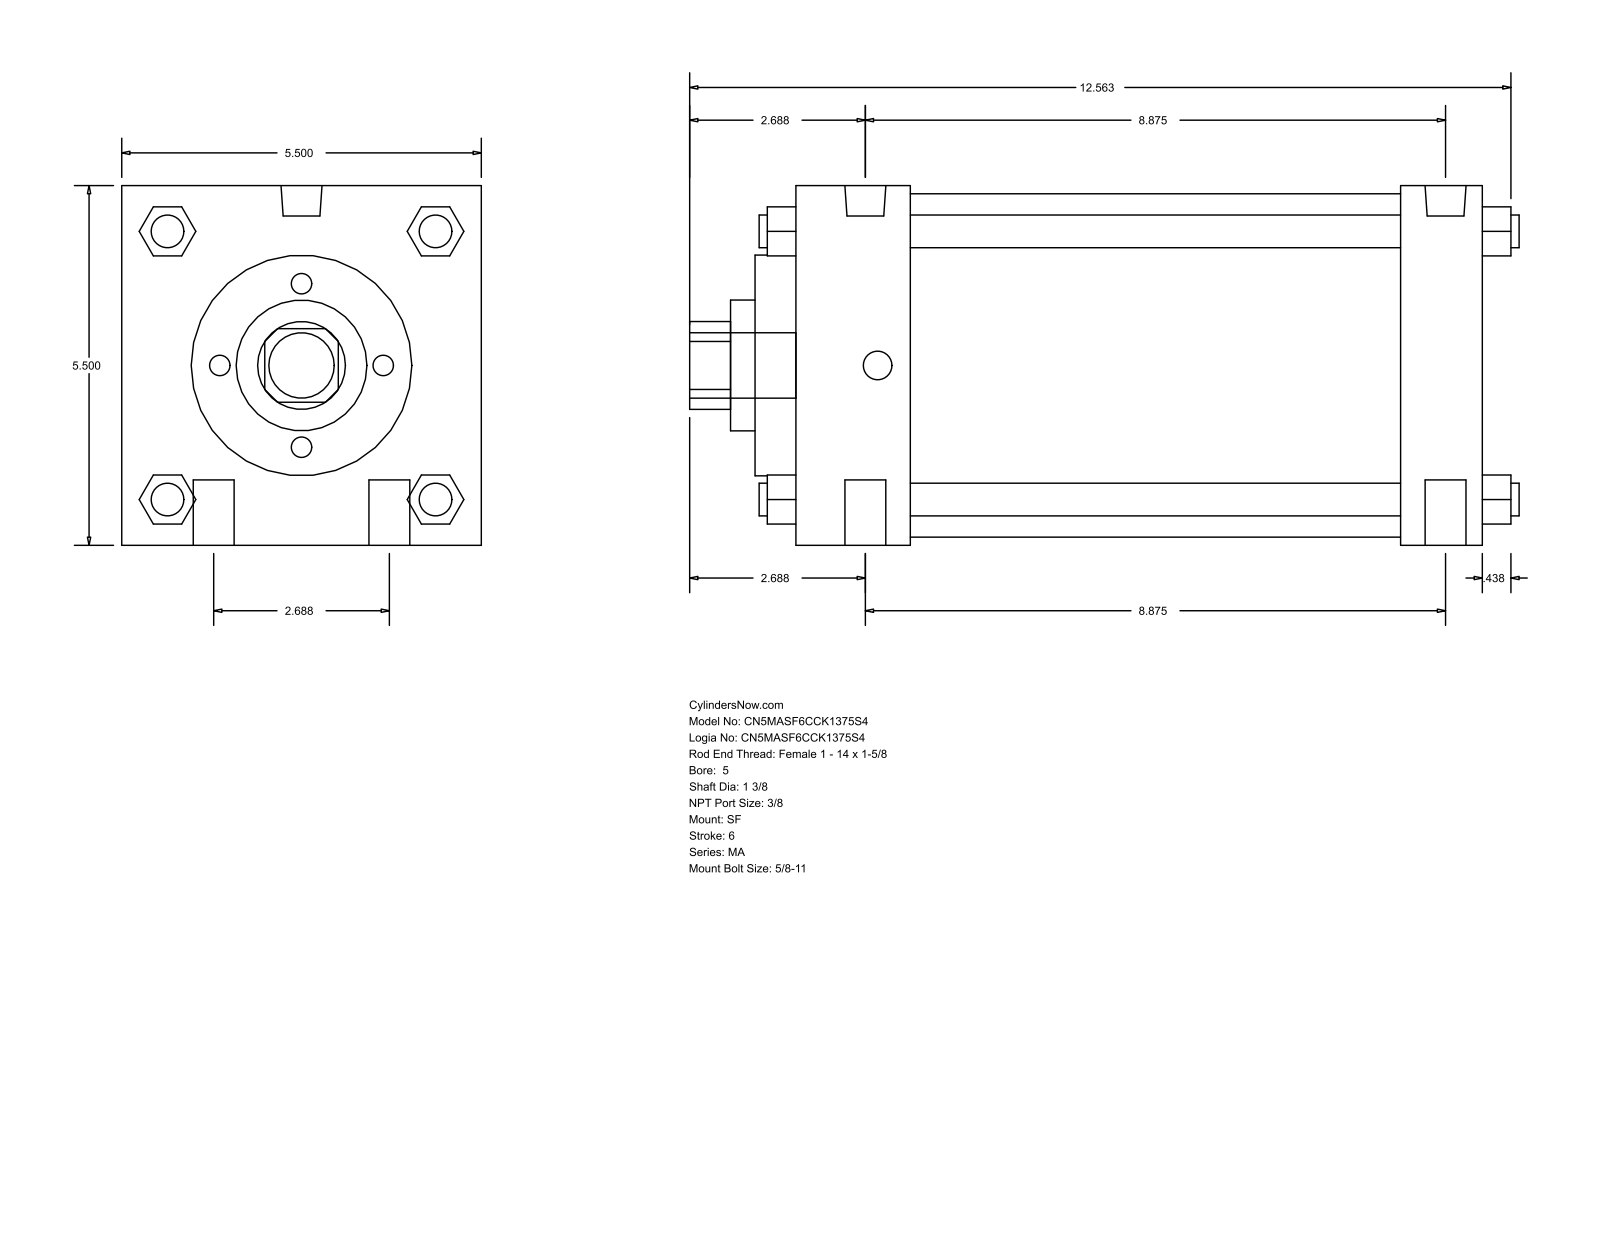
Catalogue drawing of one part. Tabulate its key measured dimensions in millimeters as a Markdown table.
| quantity | value |
| --- | --- |
| part name | MA_SF__0500_1.375 |
| STEP written by | GSSL Pune (CONFIG_CONTROL_DESIGN) |
| units | millimeters |
| bodies | 0 solids, 126 faces (95 planar, 31 cylindrical, 0 other) |
| overall size | 322.26 × 139.7 × 139.7 |
| round holes (diameter × count) | 34.92 × 1, 50.8 × 1, 85.72 × 1, 133.35 × 1 |
| round bosses / shafts (diameter × count) | 15.88 × 4, 12.7 × 4, 15.93 × 2, 11.11 × 2, 25.4 × 1 |
| partial cylindrical surfaces (radius × count) | 17.06 × 1 |
| main face-to-face distances | 139.7, 266.71, 44.45, 234.96, 190.51, 222.26, 31.75, 15.87, 60.32, 250.83 |
